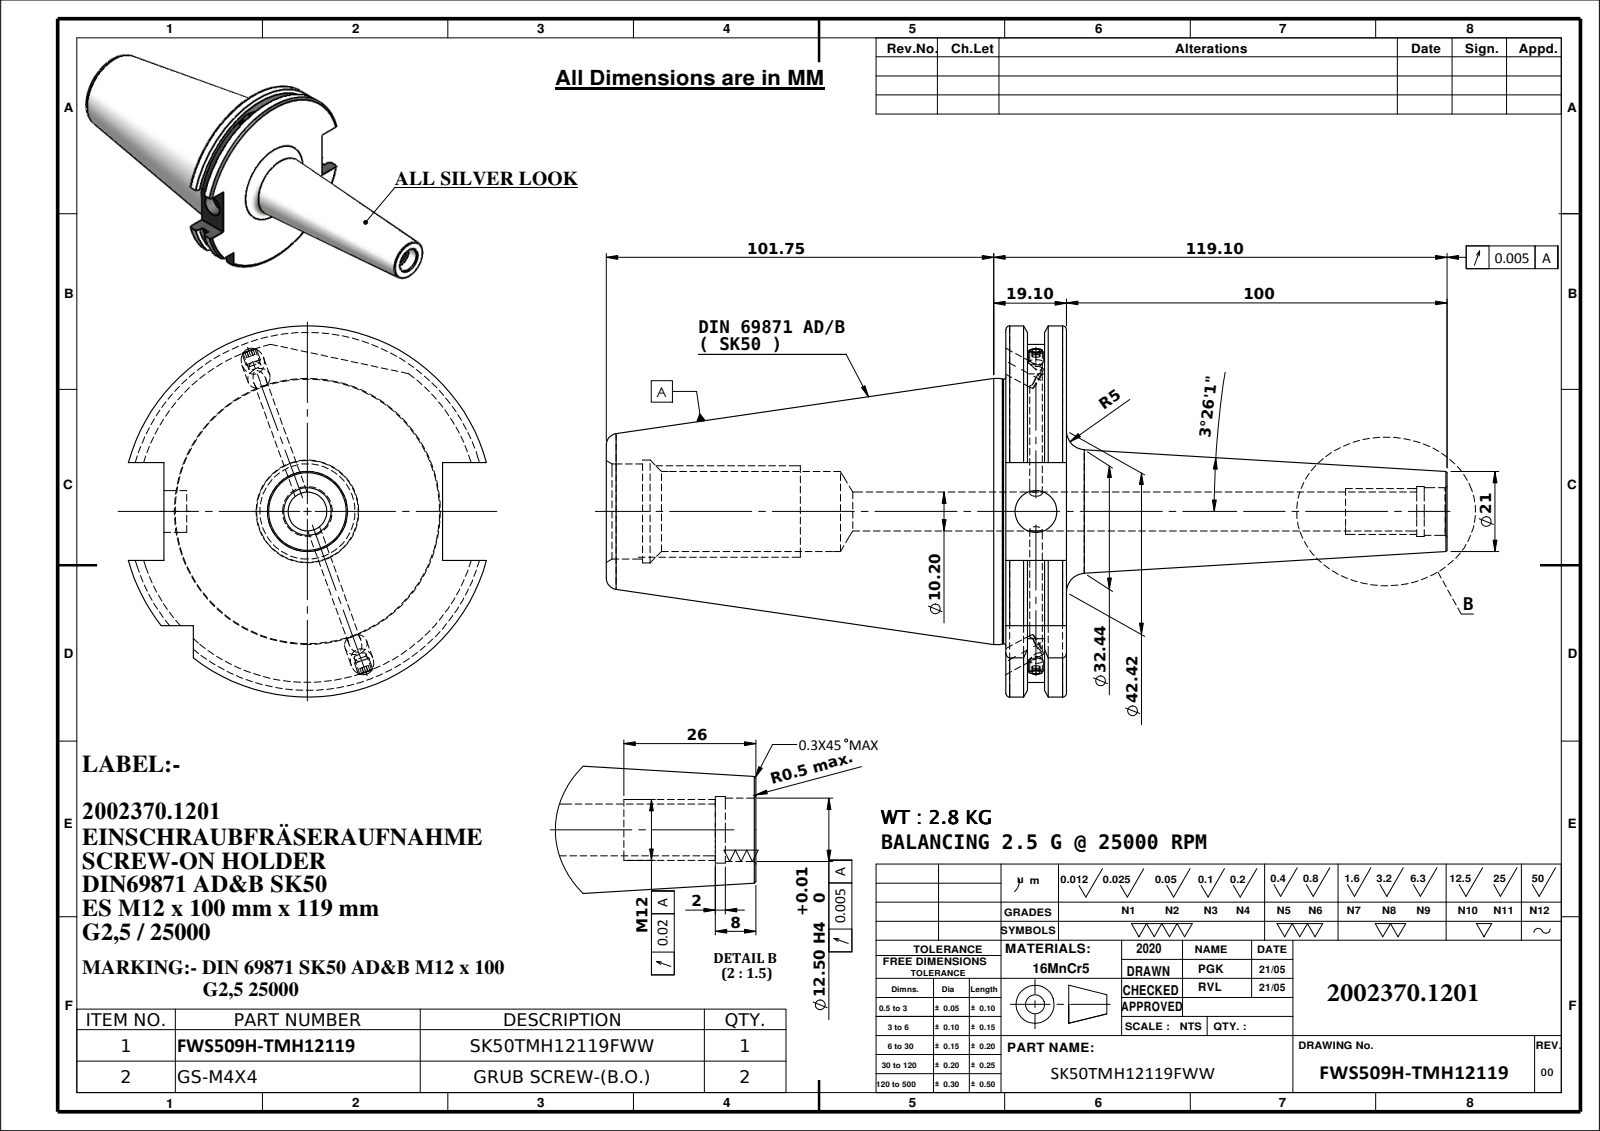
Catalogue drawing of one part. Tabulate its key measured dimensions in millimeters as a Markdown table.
| quantity | value |
| --- | --- |
| part name | 91506-ES7M12100; M4X4.IGS; SK50TMH12119FWW.IGS |
| STEP written by | SolidWorks 2018 (AUTOMOTIVE_DESIGN) |
| units | millimeters |
| bodies | 3 solids, 138 faces (0 planar, 0 cylindrical, 138 other) |
| overall size | 220.85 × 97.5 × 94.05 |
| volume | 383 266 mm³ |
| surface area | 54 634 mm² |
